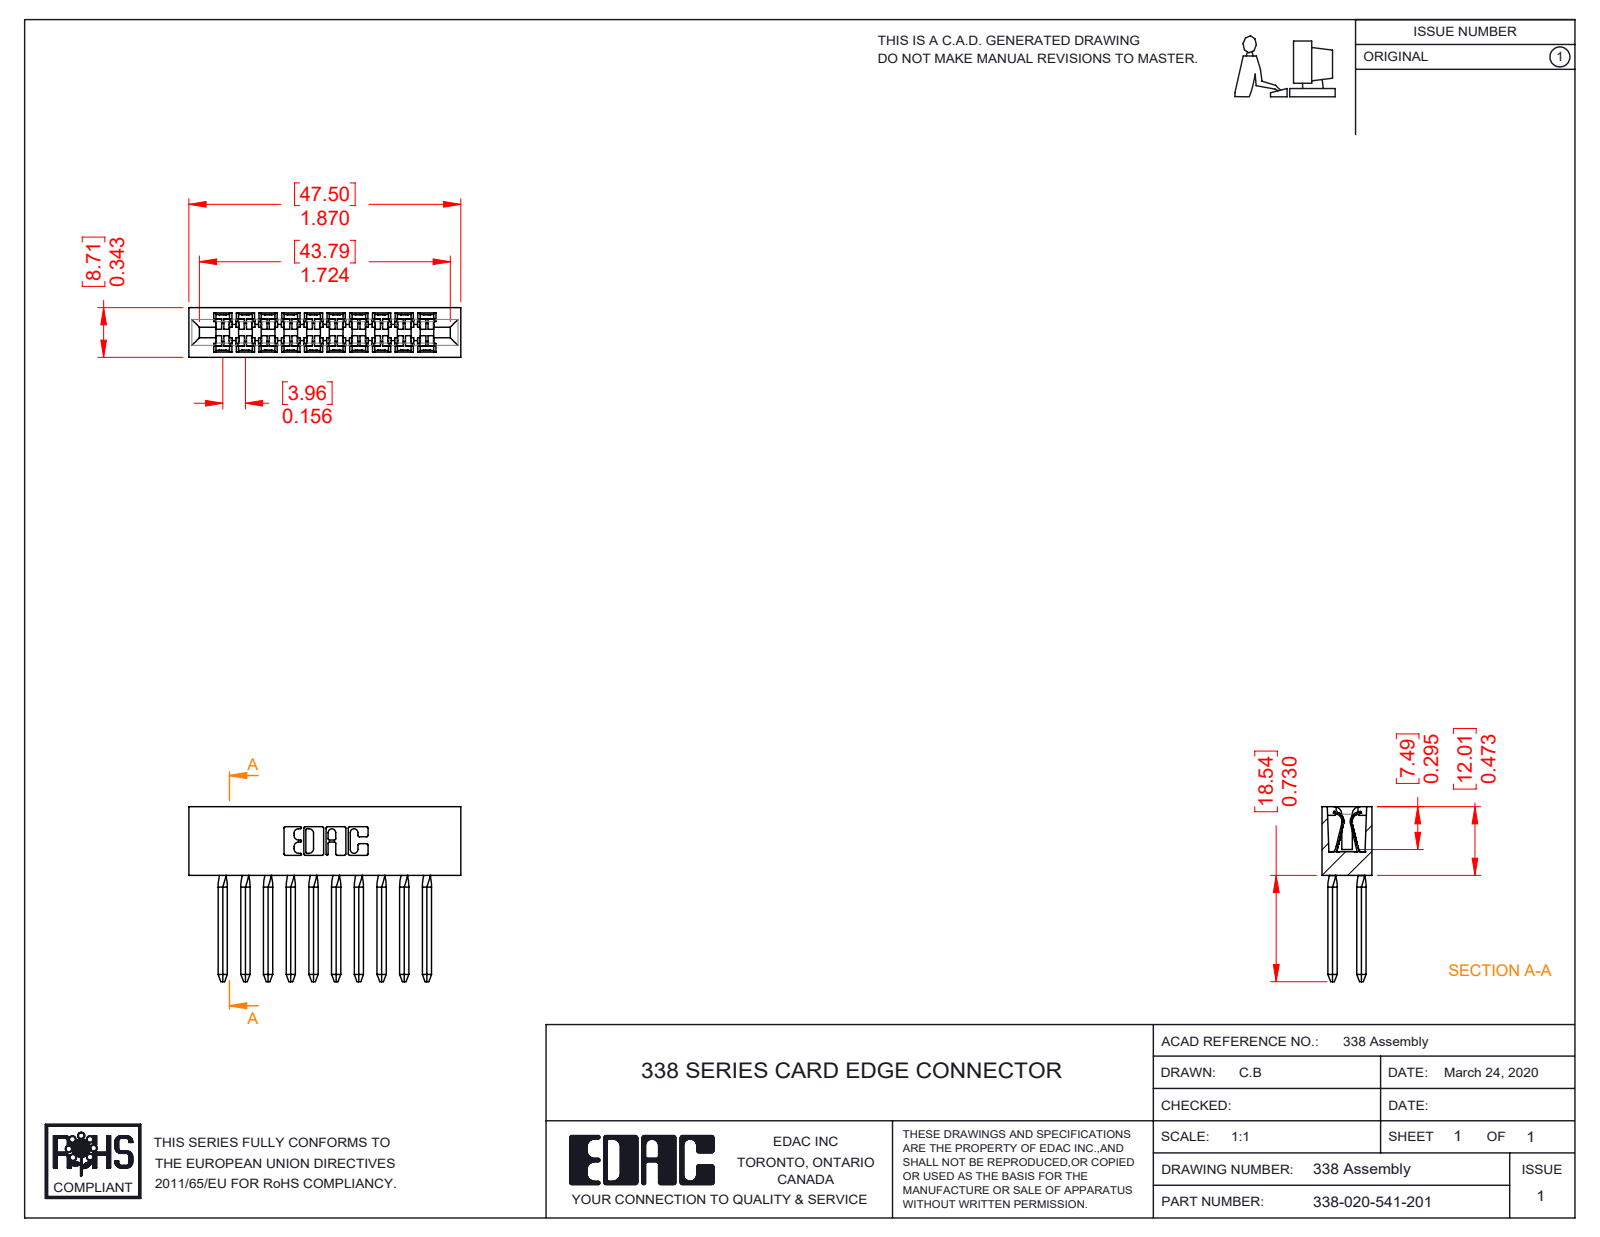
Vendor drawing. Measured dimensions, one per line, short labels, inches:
name: 338-290-001_541; 338-210-001_338-210-010-001; 338-020-541-201
written by: SolidWorks 2016 (CONFIG_CONTROL_DESIGN)
unit: in
bodies: 21 solids, 1426 faces (986 planar, 360 cylindrical, 80 other)
size: 1.87 × 1.203 × 0.343
volume: 0.239 in³; area: 10.95 in²
rounds: 62× R0.025, 22× R0.01, 20× R0.008, 16× R0.055, 16× R0.067, 16× R0.1, 6× R0.007, 6× R0.031
face distances: 0.343, 0.156, 0.11, 0.624, 0.468, 0.221, 0.312, 0.312, 0.25, 0.296
